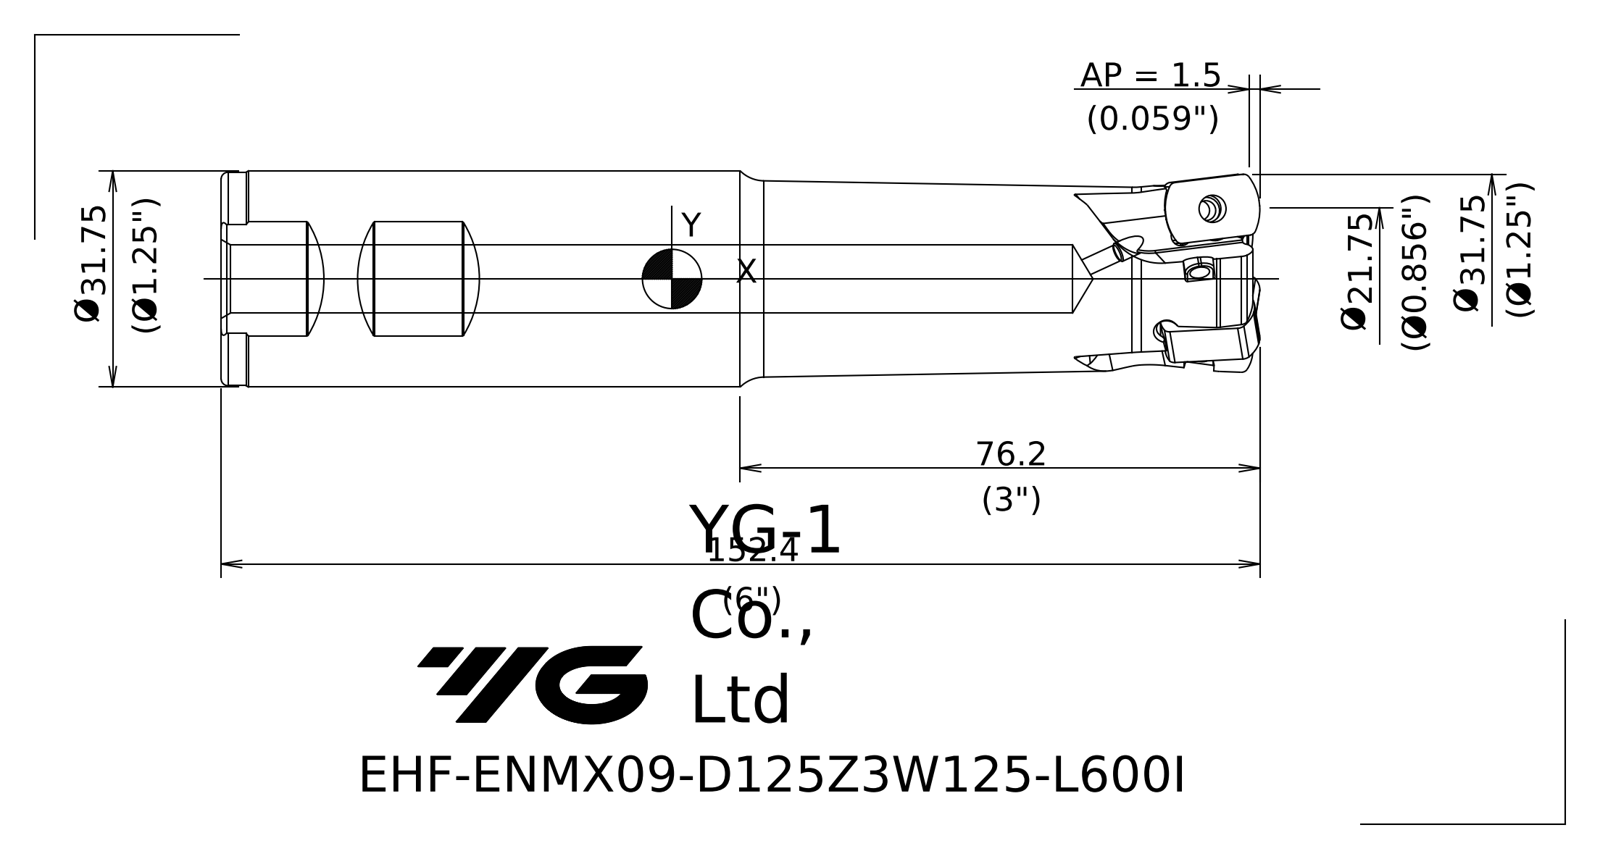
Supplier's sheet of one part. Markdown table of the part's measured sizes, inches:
| quantity | value |
| --- | --- |
| part name | 120185C07CB1h81y |
| STEP written by | SIEMENS PLM Software NX 10.0 (AP203_CONFIGURATION_CONTROLLED_3D_DESIGN_OF_MECHANICAL_PARTS_AND_ASSEMBLIES_MIM_LF) |
| units | inches |
| bodies | 2 solids, 54 faces (9 planar, 7 cylindrical, 38 other) |
| overall size | 6.001 × 1.25 × 1.25 |
| volume | 4.794 in³ |
| surface area | 30.71 in² |
| round holes (diameter × count) | 0.059 × 1, 0.394 × 1 |
| round bosses / shafts (diameter × count) | 1.25 × 1, 1.234 × 1 |
| partial cylindrical surfaces (radius × count) | 0.012 × 3 |
| main face-to-face distances | 5.922, 0.635, 0.967, 0.331, 0.056, 5.866 |
